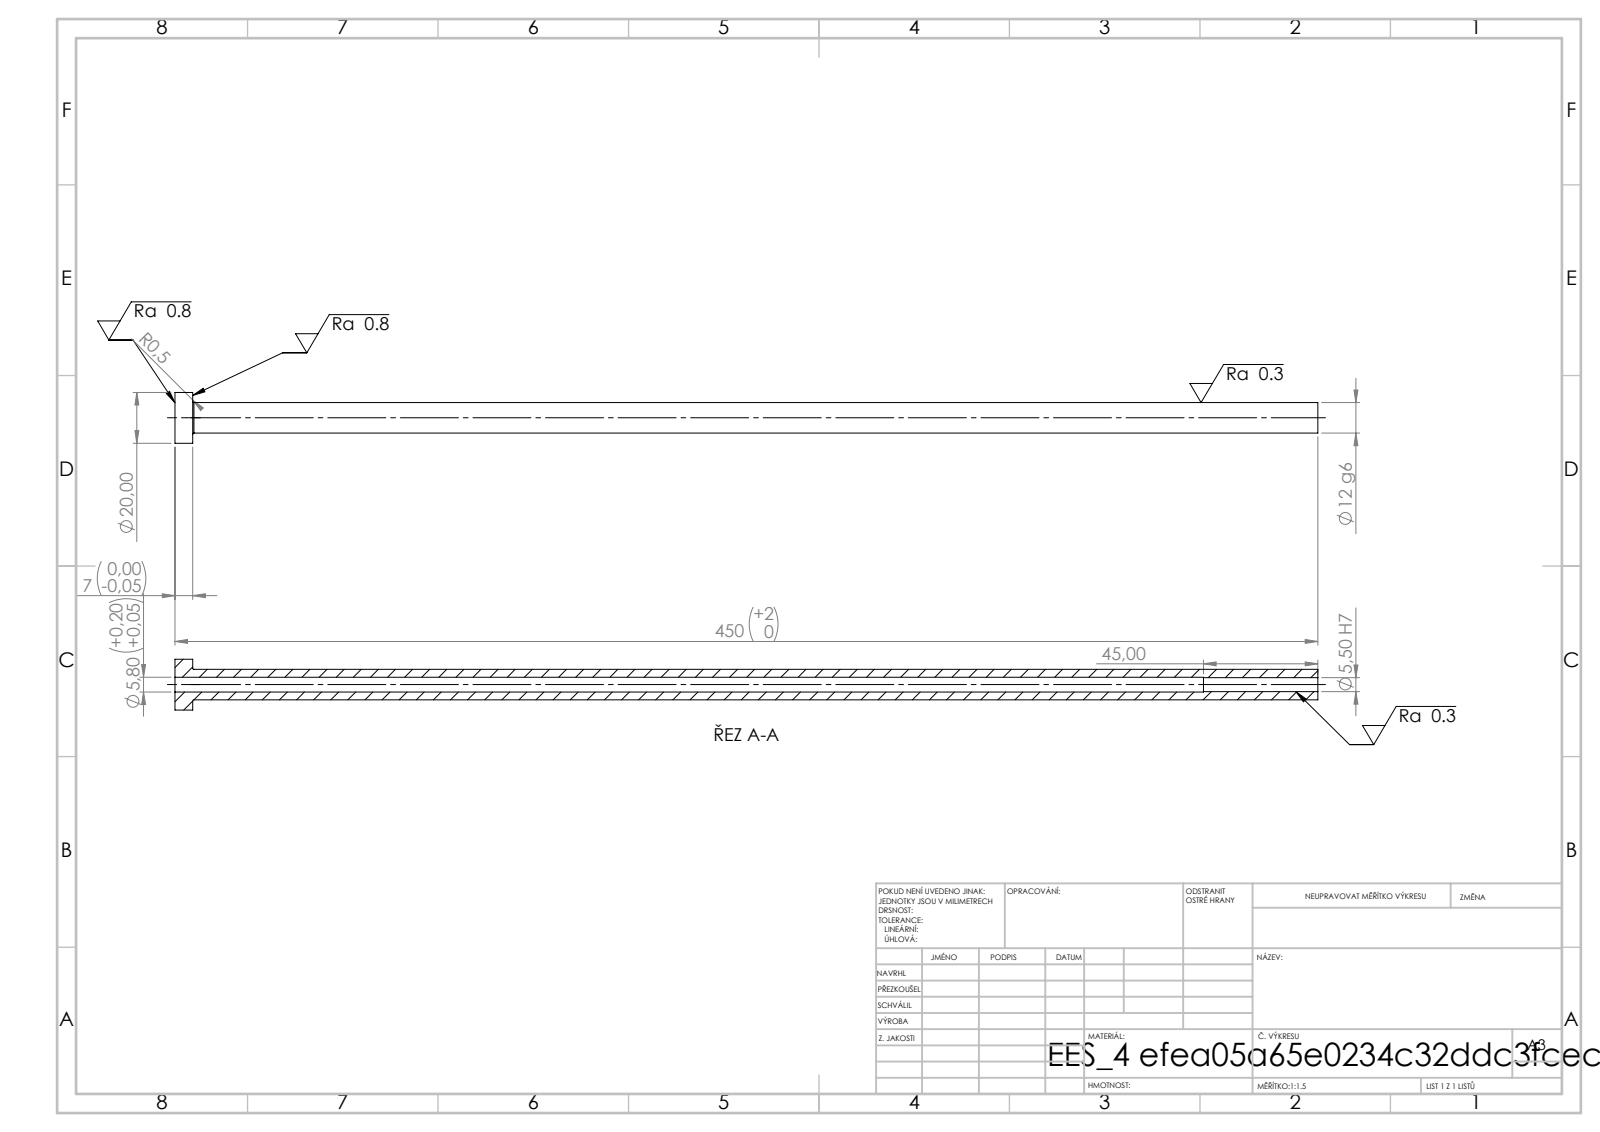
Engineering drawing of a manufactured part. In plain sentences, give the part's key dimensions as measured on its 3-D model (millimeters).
Its 3-D file was written by "SolidWorks 2019 (CONFIG_CONTROL_DESIGN)". It is 1 solid with 14 faces: 4 planar, 8 cylindrical and 2 other. Overall it measures 450 by 20 by 20 millimeters. Its volume is 40 534 cubic millimeters and its surface area 25 870 square millimeters. Round holes: 1 of diameter 5.5, 1 of diameter 5.8. Round bosses or shafts: 1 of diameter 20, 1 of diameter 12. The main face-to-face distances are 7, 450, 443, 405, 398, 45.
